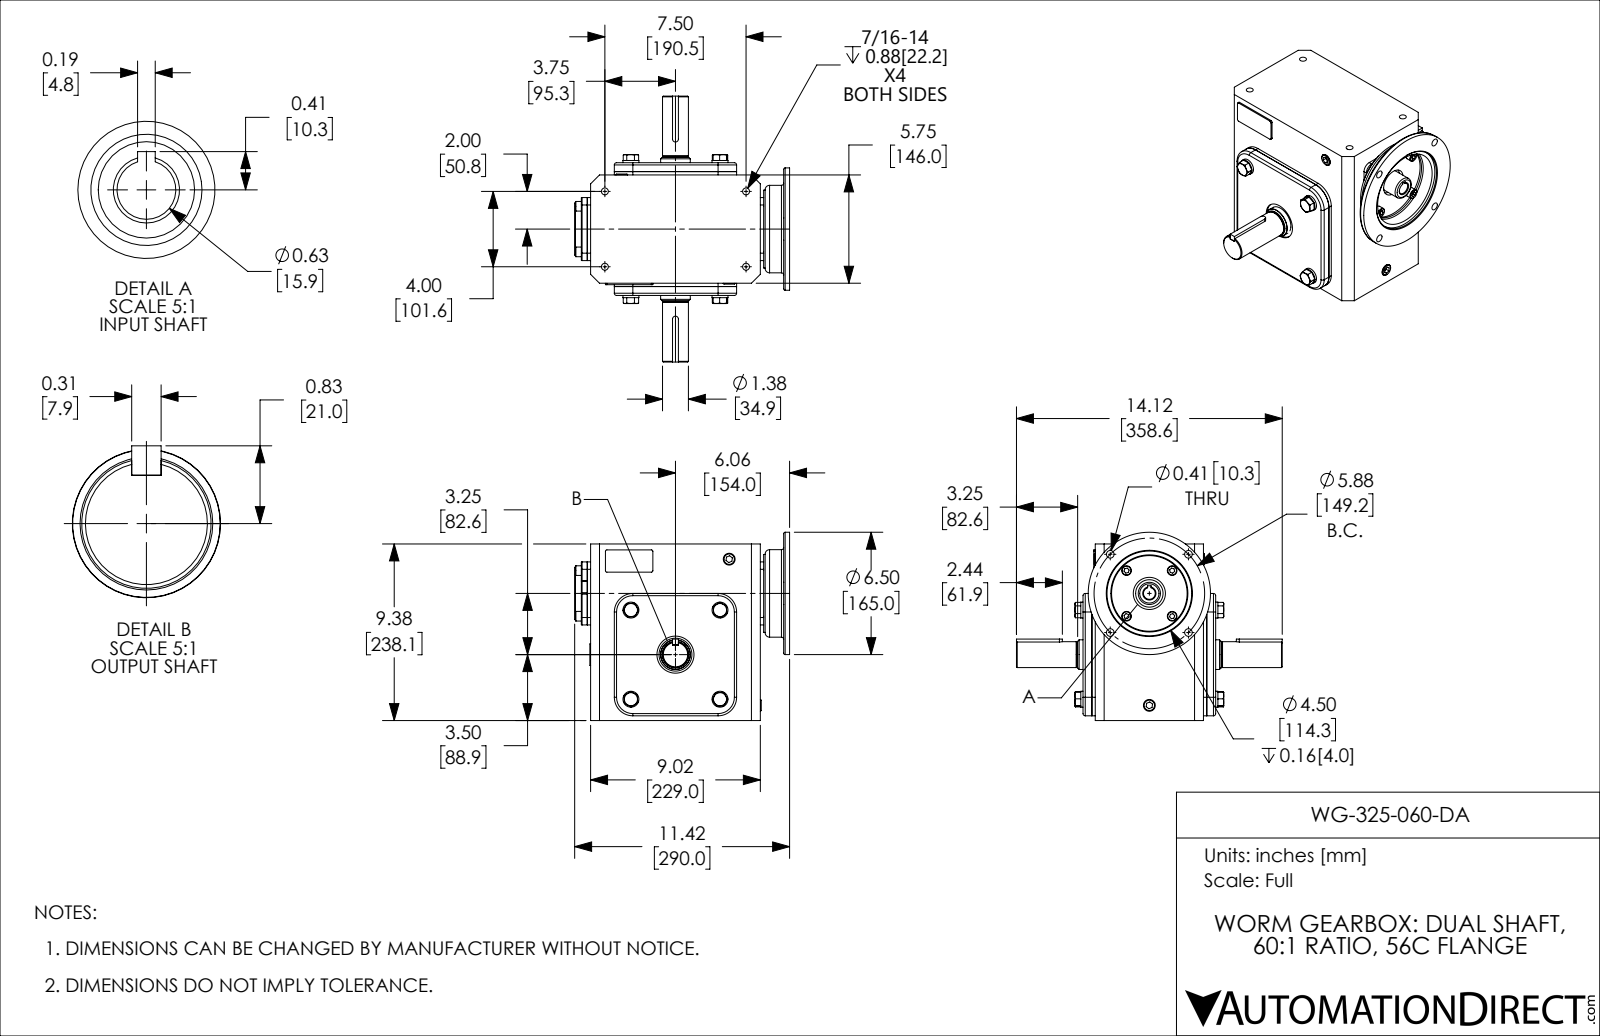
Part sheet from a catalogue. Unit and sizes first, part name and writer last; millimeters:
Units: millimetres
Overall size (bounding box): 358.6 × 290 × 253.9
Round holes (diameter × count): ⌀9.3 ×4, ⌀10.3 ×4, ⌀16 ×3, ⌀15 ×1, ⌀15.9 ×1, ⌀24.8 ×1, ⌀30 ×1, ⌀37 ×1, ⌀50 ×1, ⌀62 ×1, ⌀70 ×1, ⌀102 ×1
Round bosses / shafts (diameter × count): ⌀21.5 ×4, ⌀13 ×4, ⌀165 ×1, ⌀118 ×1, ⌀105 ×1, ⌀72 ×1, ⌀40 ×1, ⌀34.9 ×1
Partial cylindrical surfaces — rounded edges, fillets, slot ends (radius × count): R3 ×8, R2 ×7, R10 ×4, R23 ×4, R25 ×4, R0.5 ×2, R1 ×2, R4 ×2
Main face-to-face distances: 2, 4.5, 165, 10, 177, 12, 167, 162.5, 14.5, 16.5
Hole centre spacings: 74.6, 105.5, 60.6, 101.6, 111.5, 145.2, 147.8, 149.2
Volume: 8 451 000 mm³ · Surface area: 604 200 mm²
Bodies: 42 solids, 612 faces (331 planar, 178 cylindrical, 103 other)
Part name (STEP PRODUCT): WG-325-060-DA
STEP written by: SolidWorks 2017 (AUTOMOTIVE_DESIGN)
